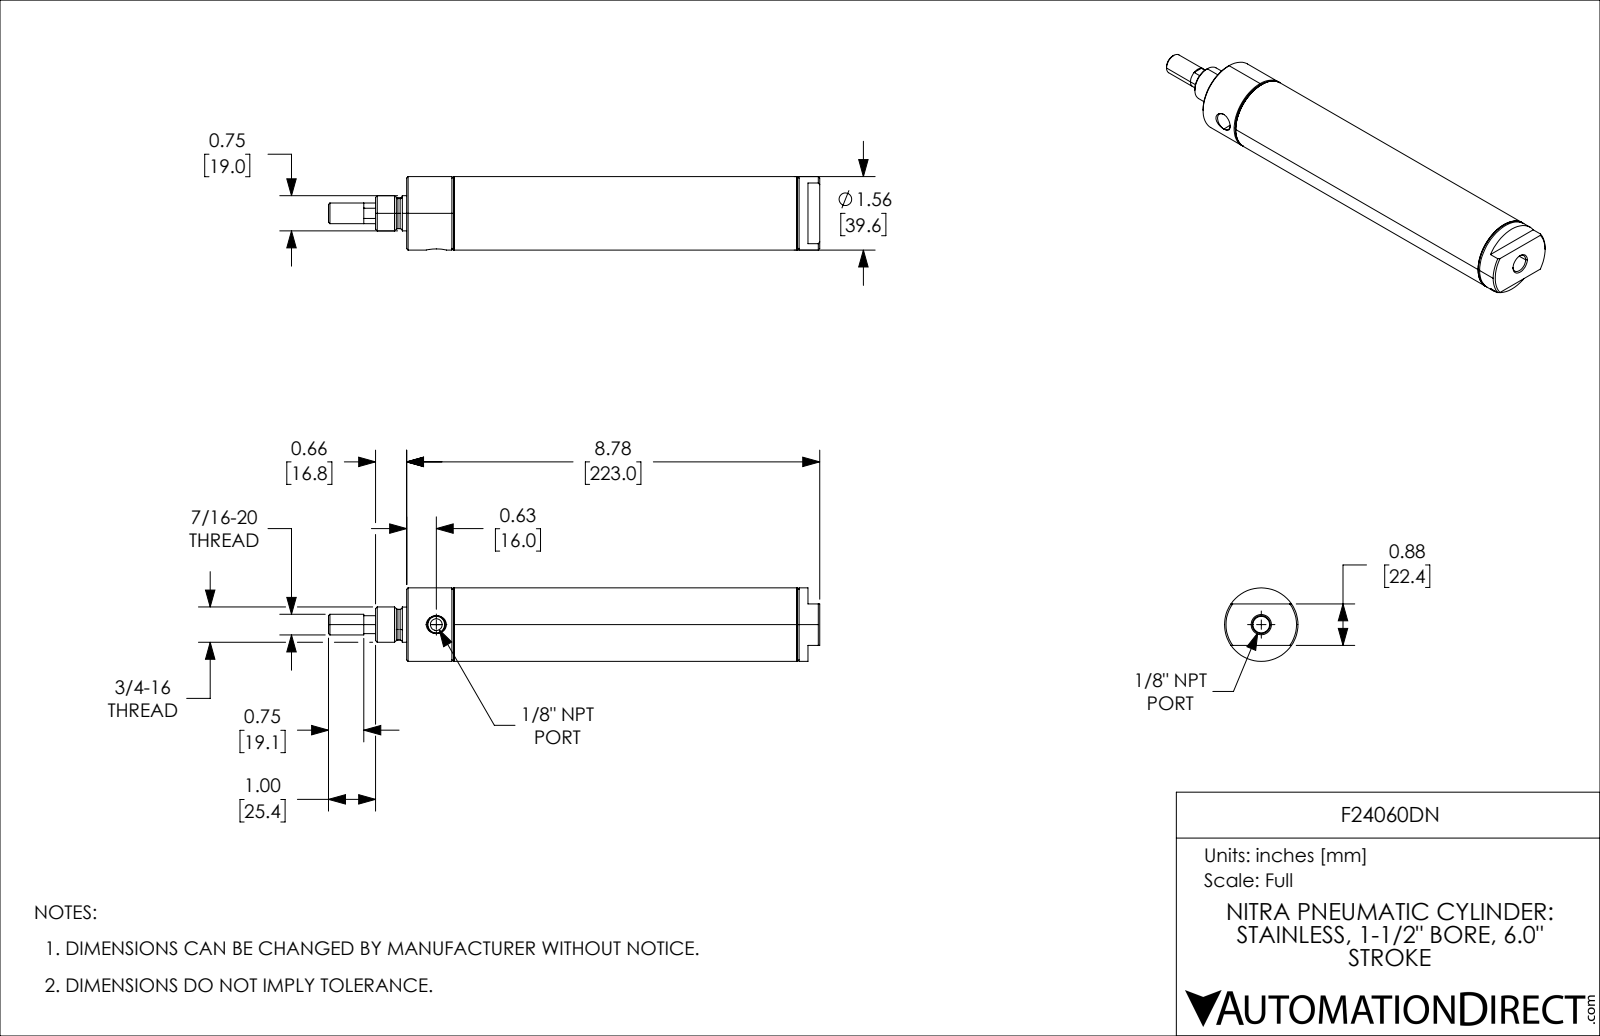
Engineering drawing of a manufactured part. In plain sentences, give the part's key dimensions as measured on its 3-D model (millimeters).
The part is named "F24060DN; F24060DN_5; F24060DN_3; F24060DN_9 (+1 more)". Its 3-D file was written by "SolidWorks 2021 (CONFIG_CONTROL_DESIGN)". It is 4 solids with 126 faces: 28 planar, 42 cylindrical and 56 other. Overall it measures 265.12 by 39.62 by 39.62 millimeters. Its volume is 112 306 cubic millimeters and its surface area 74 169 square millimeters. Round holes: 1 of diameter 6.35, 1 of diameter 11.73, 1 of diameter 24.71, 1 of diameter 36.36. Round bosses or shafts: 1 of diameter 39.62, 1 of diameter 38.39, 1 of diameter 19.05, 1 of diameter 18.99, 1 of diameter 16.6, 1 of diameter 11.13, 1 of diameter 11.11. The main face-to-face distances are 22.22, 6.35, 11.13, 152.4, 174.62, 30.86, 183.26, 205.48, 222.96, 192.1.
